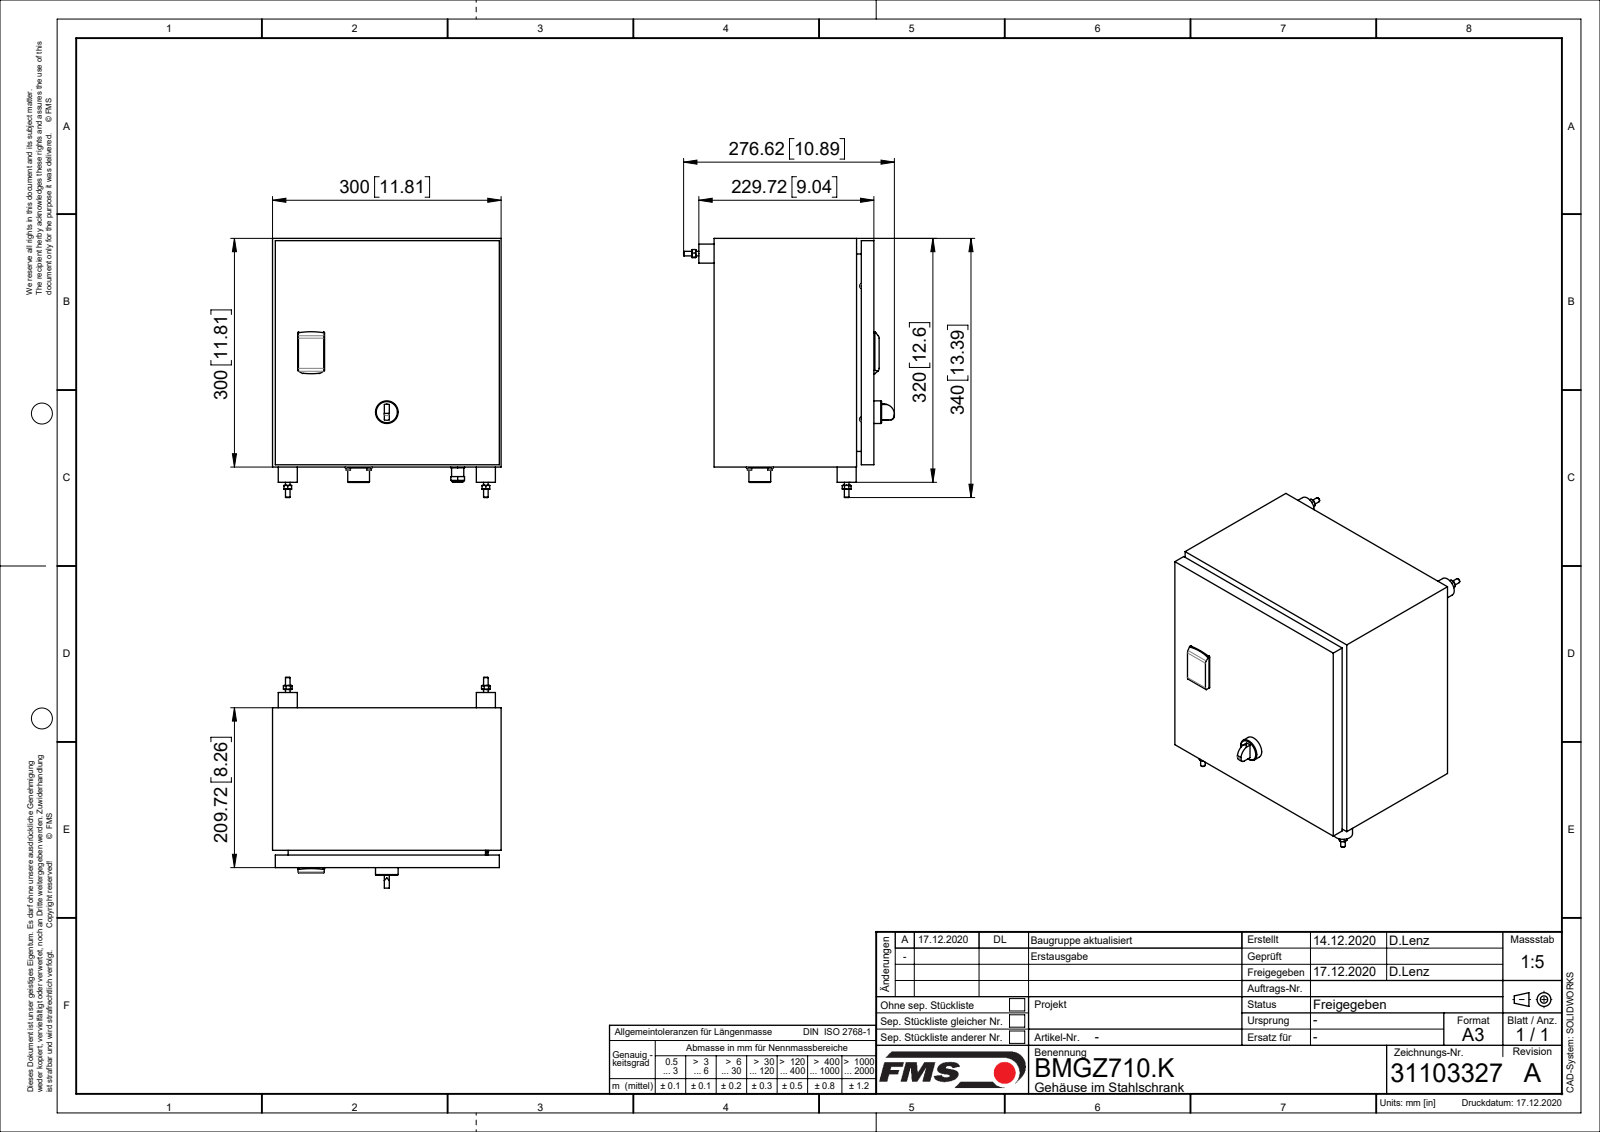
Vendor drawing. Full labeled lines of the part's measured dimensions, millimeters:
Part name (STEP PRODUCT): 31102876_01; 6kt-Mu ISO4032_M4; 31102875_01; 31102887_01 (+8 more)
STEP written by: SolidWorks 2018 (CONFIG_CONTROL_DESIGN)
Units: millimetres
Bodies: 110 solids, 16355 faces (9318 planar, 4508 cylindrical, 2529 other)
Overall size (bounding box): 340 × 300 × 276.62
Volume: 1 617 000 mm³ · Surface area: 1 605 000 mm²
Round holes (diameter × count): ⌀0.99 ×32, ⌀1 ×32, ⌀1.2 ×18, ⌀1.4 ×17, ⌀3.3 ×14, ⌀1.1 ×10, ⌀2.4 ×8, ⌀3 ×8, ⌀4.5 ×8, ⌀6 ×8, ⌀8 ×8, ⌀4.4 ×6
Round bosses / shafts (diameter × count): ⌀0.6 ×60, ⌀5.5 ×20, ⌀4 ×12, ⌀0.63 ×12, ⌀2 ×11, ⌀3 ×9, ⌀7 ×8, ⌀1.4 ×8
Partial cylindrical surfaces — rounded edges, fillets, slot ends (radius × count): R0.2 ×605, R0.3 ×489, R0.1 ×313, R0.5 ×287, R1 ×259, R0.45 ×72, R0.15 ×49, R0.25 ×41
Main face-to-face distances: 1.25, 298.75, 1.5, 209.72, 208.47, 17.25, 16, 2.5, 18.5, 19.75
Hole centre spacings: 21, 45.5, 40, 28.29, 2.5, 24.5, 66.5, 2.49
